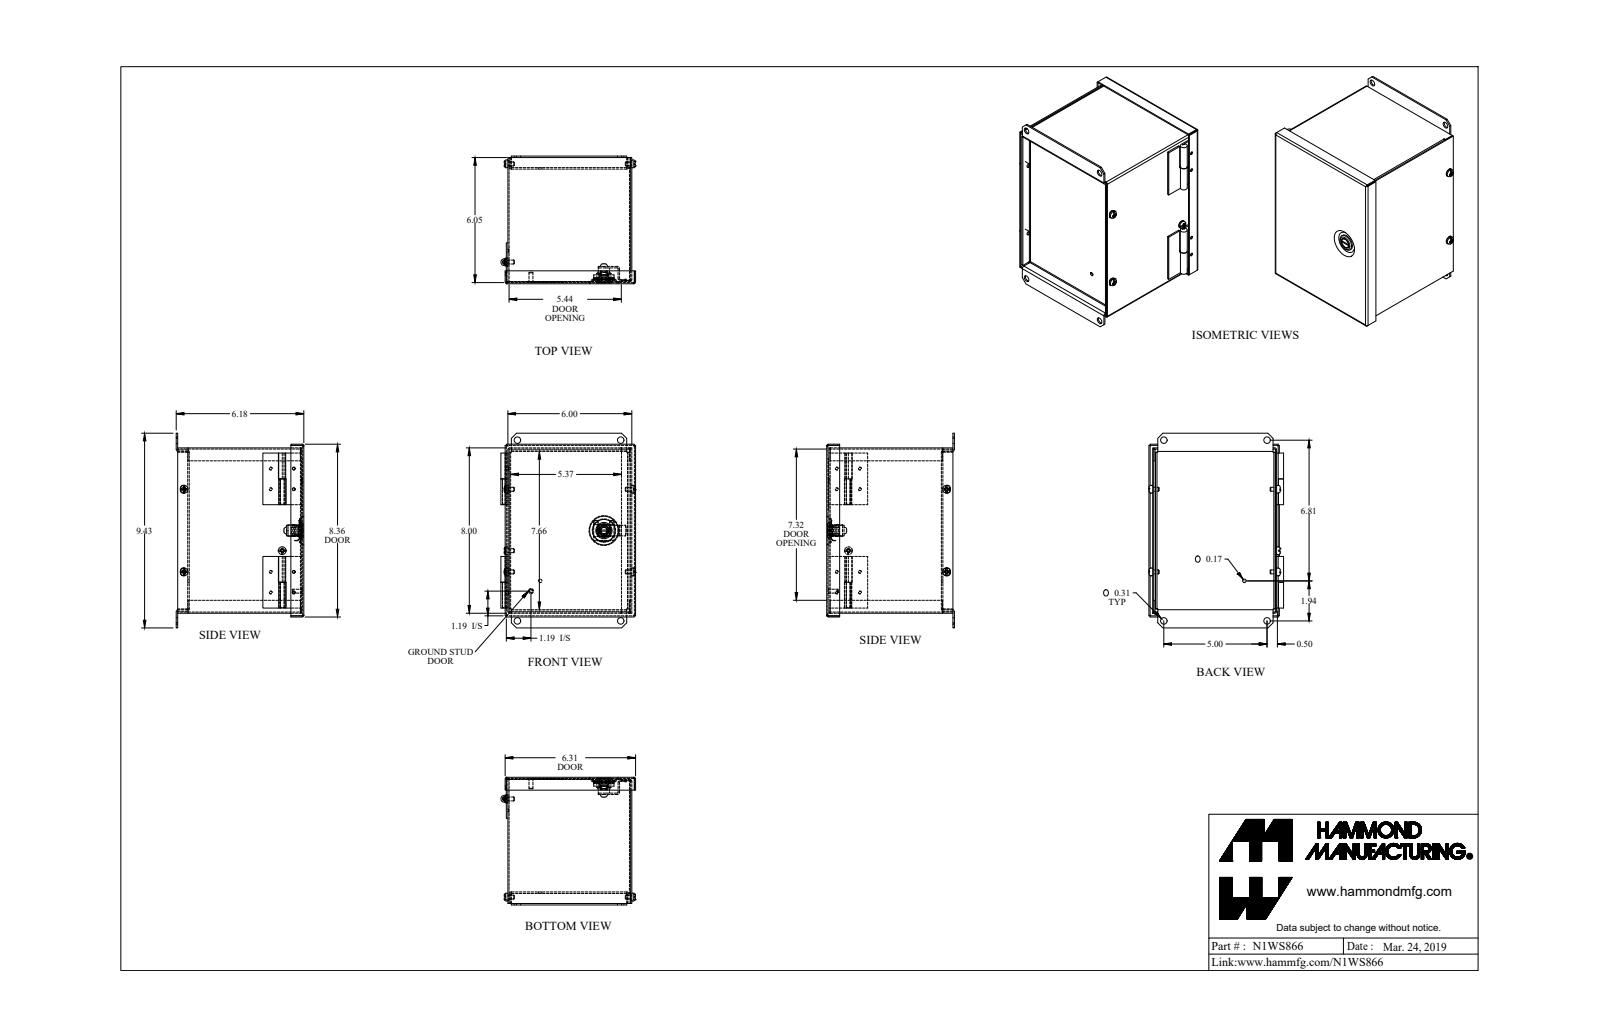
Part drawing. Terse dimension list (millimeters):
name: N1WS866
written by: SolidWorks 2018 (AUTOMOTIVE_DESIGN)
unit: mm
bodies: 15 solids, 539 faces (290 planar, 196 cylindrical, 53 other)
size: 239.4 × 165.6 × 156.9
volume: 329 400 mm³; area: 430 500 mm²
holes: 8× ⌀3.6, 4× ⌀4.3, 4× ⌀7.9, 1× ⌀4.7, 1× ⌀8.1, 1× ⌀12.1
bosses: 8× ⌀3.3, 3× ⌀9.5, 3× ⌀4.8, 1× ⌀20, 1× ⌀13.9, 1× ⌀12, 1× ⌀11.9, 1× ⌀9.3
rounds: 9× R0.7, 9× R2.2, 8× R0.9, 6× R2.7, 4× R0.3, 4× R2.5, 4× R2.8, 2× R2
face distances: 1.4, 151, 201.8, 1.8, 1.4, 152.4, 149.5, 142.8, 141.3, 139.5
hole spacings: 127, 25.4, 28.4, 38.1, 130.1, 101.6, 105.5, 106.6
